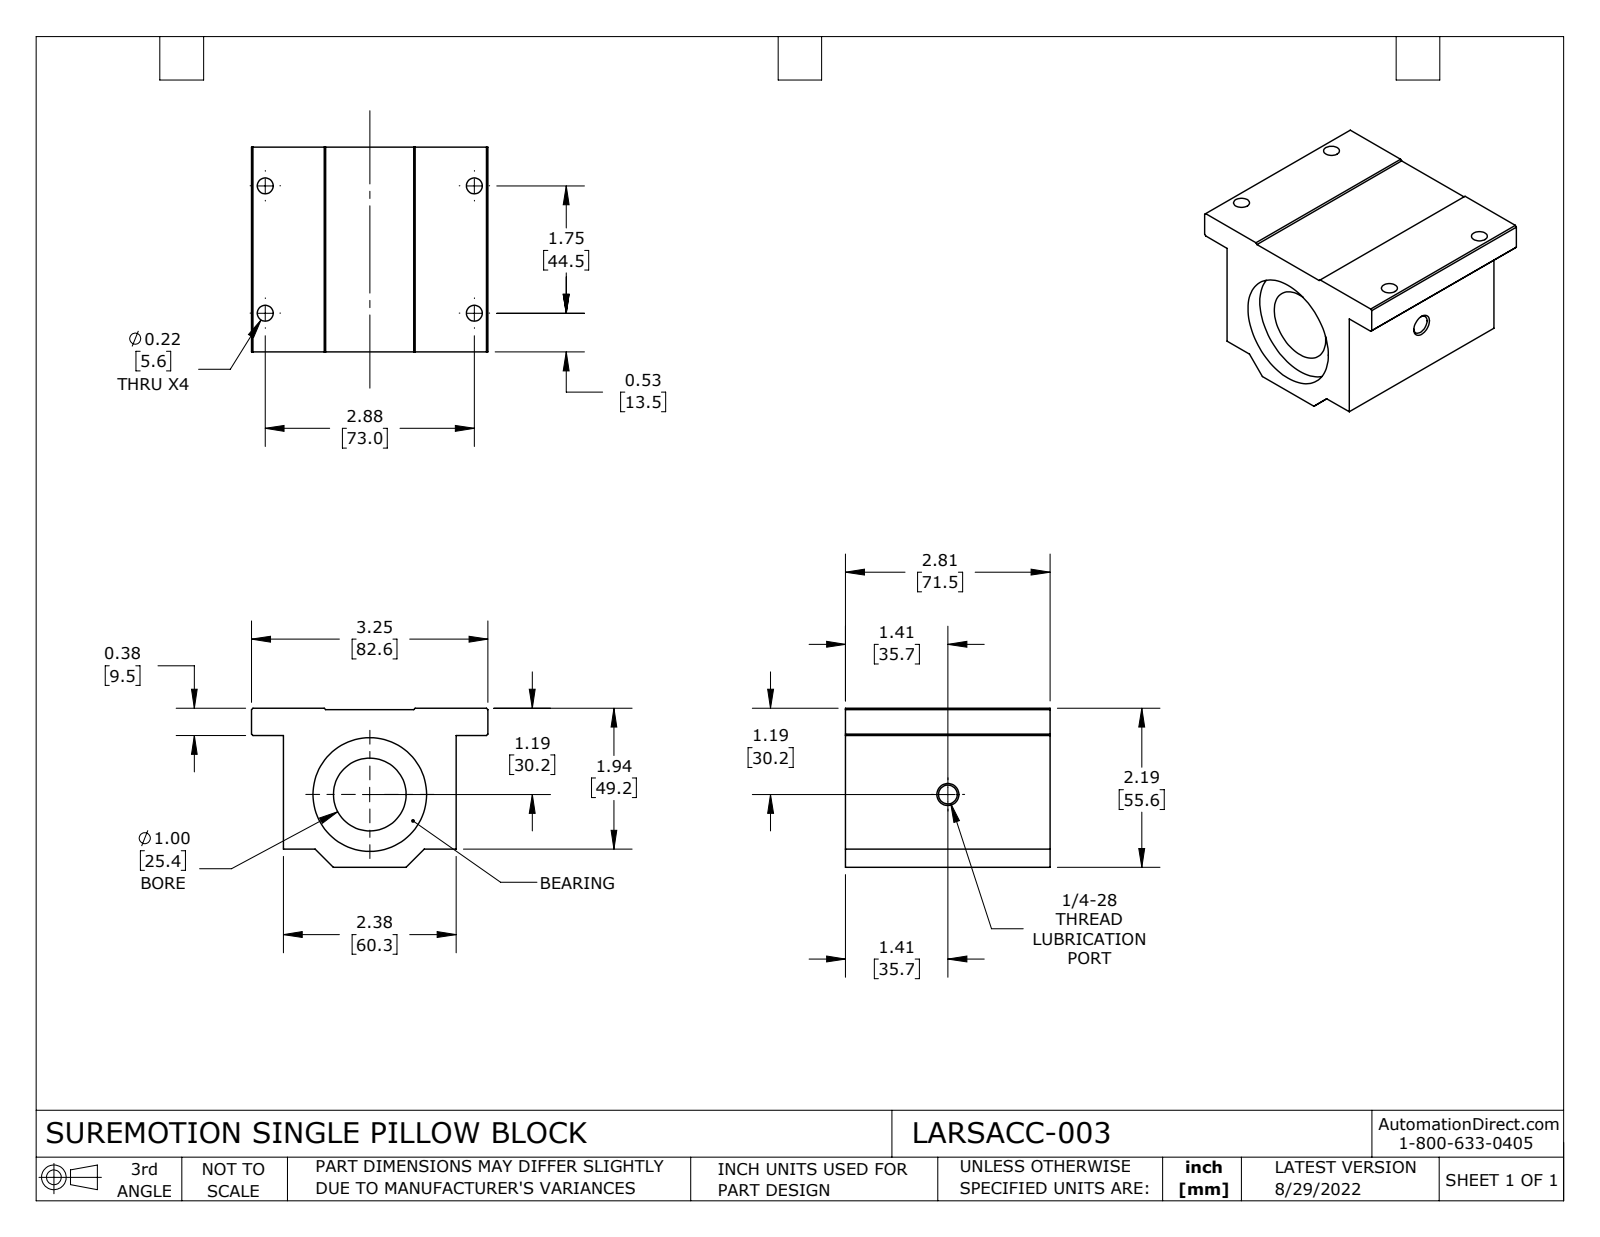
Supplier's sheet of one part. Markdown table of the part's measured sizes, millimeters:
| quantity | value |
| --- | --- |
| part name | LARSACC-003 |
| STEP written by | SolidWorks 2021 (CONFIG_CONTROL_DESIGN) |
| units | millimeters |
| bodies | 1 solid, 43 faces (25 planar, 16 cylindrical, 2 other) |
| overall size | 82.6 × 71.5 × 55.6 |
| volume | 194 500 mm³ |
| surface area | 31 830 mm² |
| round holes (diameter × count) | 5.6 × 4, 6.6 × 1, 25.4 × 1, 39.7 × 1 |
| main face-to-face distances | 71.5, 60.4, 0.5, 55.1, 55.6, 6.4, 48.7, 49.2, 5.8, 65.6 |
| hole center spacings | 44.5, 73, 85.5 |
